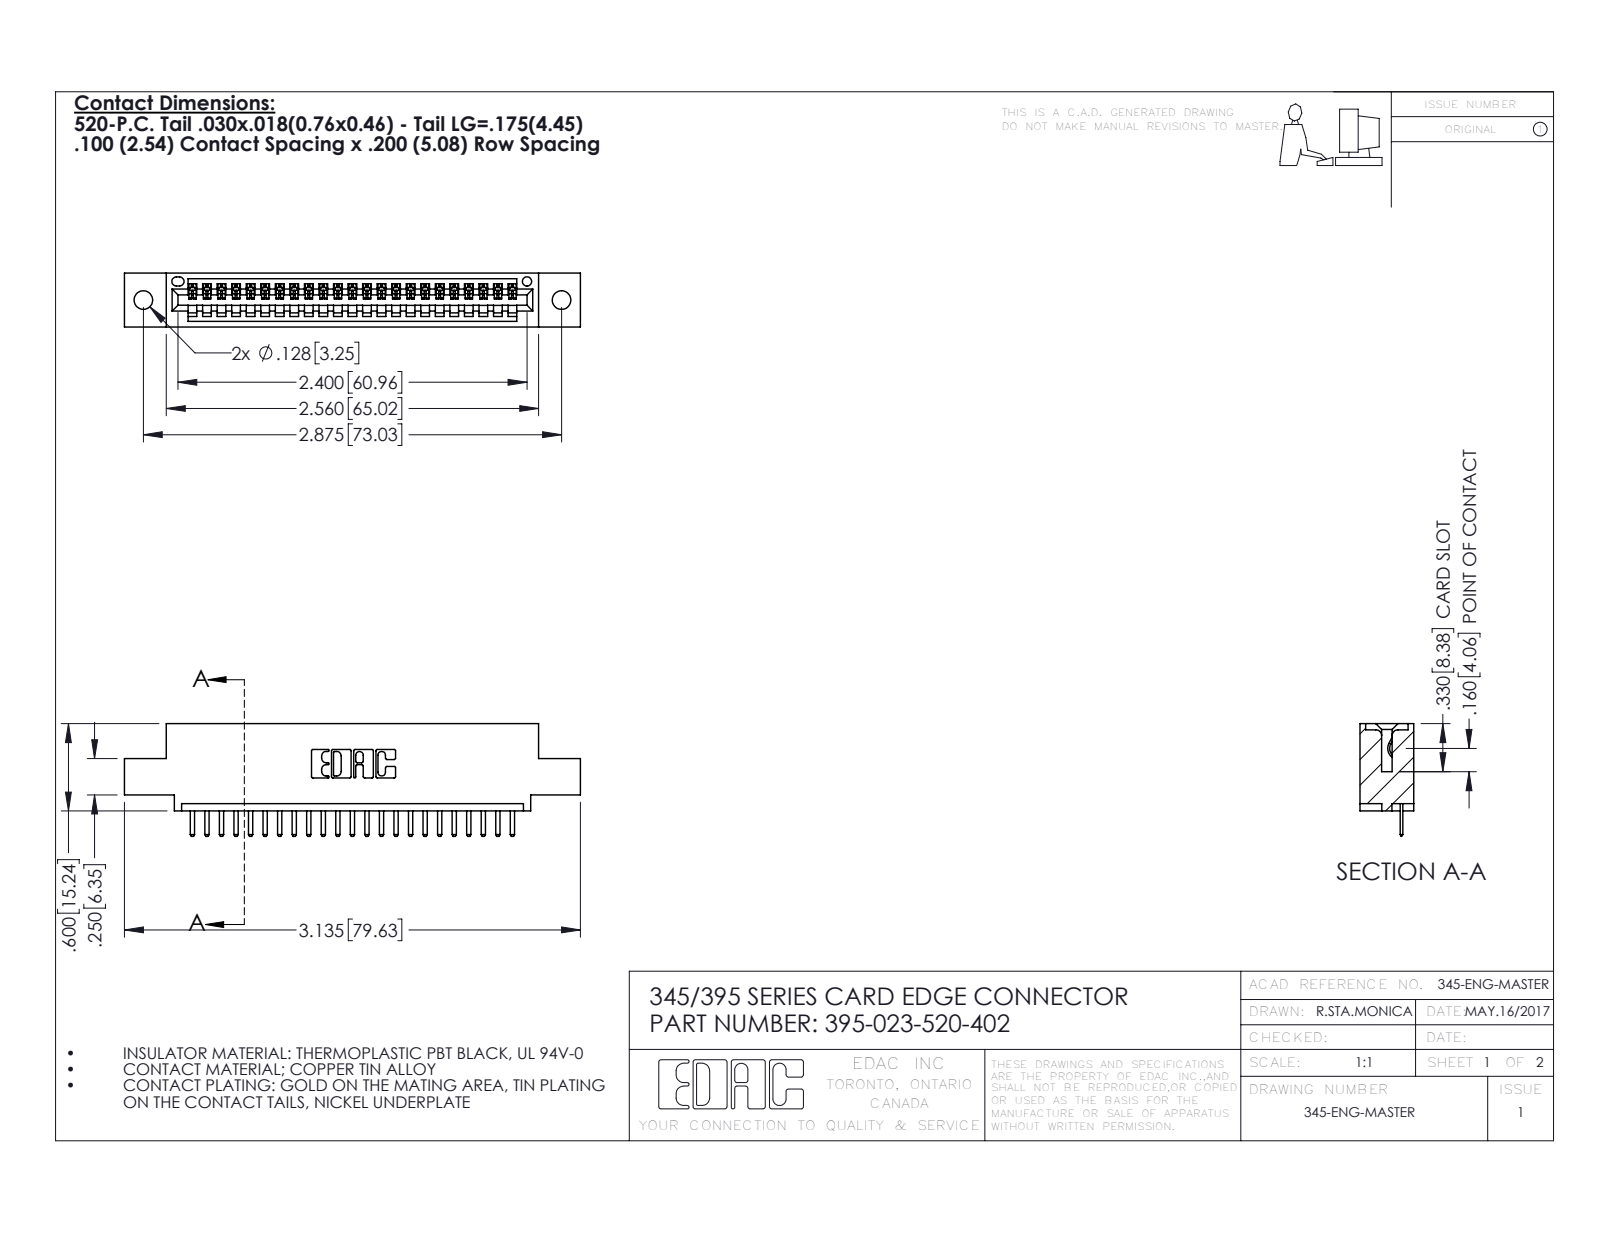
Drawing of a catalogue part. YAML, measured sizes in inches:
part_name: "345 Part_0.110 Offset - 0.128 Dia; 395-023-520-402; 345-292-001_345-293-120"
step_written_by: "SolidWorks 2016 (CONFIG_CONTROL_DESIGN)"
units: inches
bodies: {solids: 24, faces: 1556, planar: 1050, cylindrical: 506, other: 0}
overall_size: [3.135, 0.775, 0.37]
volume: 0.441
surface_area: 13.87
round_holes:
  - {diameter: 0.128, count: 2}
  - {diameter: 0.064, count: 1}
partial_cylinders:
  - {radius: 0.01, count: 48}
  - {radius: 0.006, count: 46}
  - {radius: 0.01, count: 22}
  - {radius: 0.007, count: 6}
  - {radius: 0.031, count: 6}
  - {radius: 0.026, count: 3}
  - {radius: 0.031, count: 2}
  - {radius: 0.04, count: 2}
face_to_face_distances: [0.298, 0.072, 0.37, 0.2, 0.098, 0.272, 0.025, 0.225, 0.072, 0.149]
hole_center_spacings: [0.27, 2.641, 2.875]
